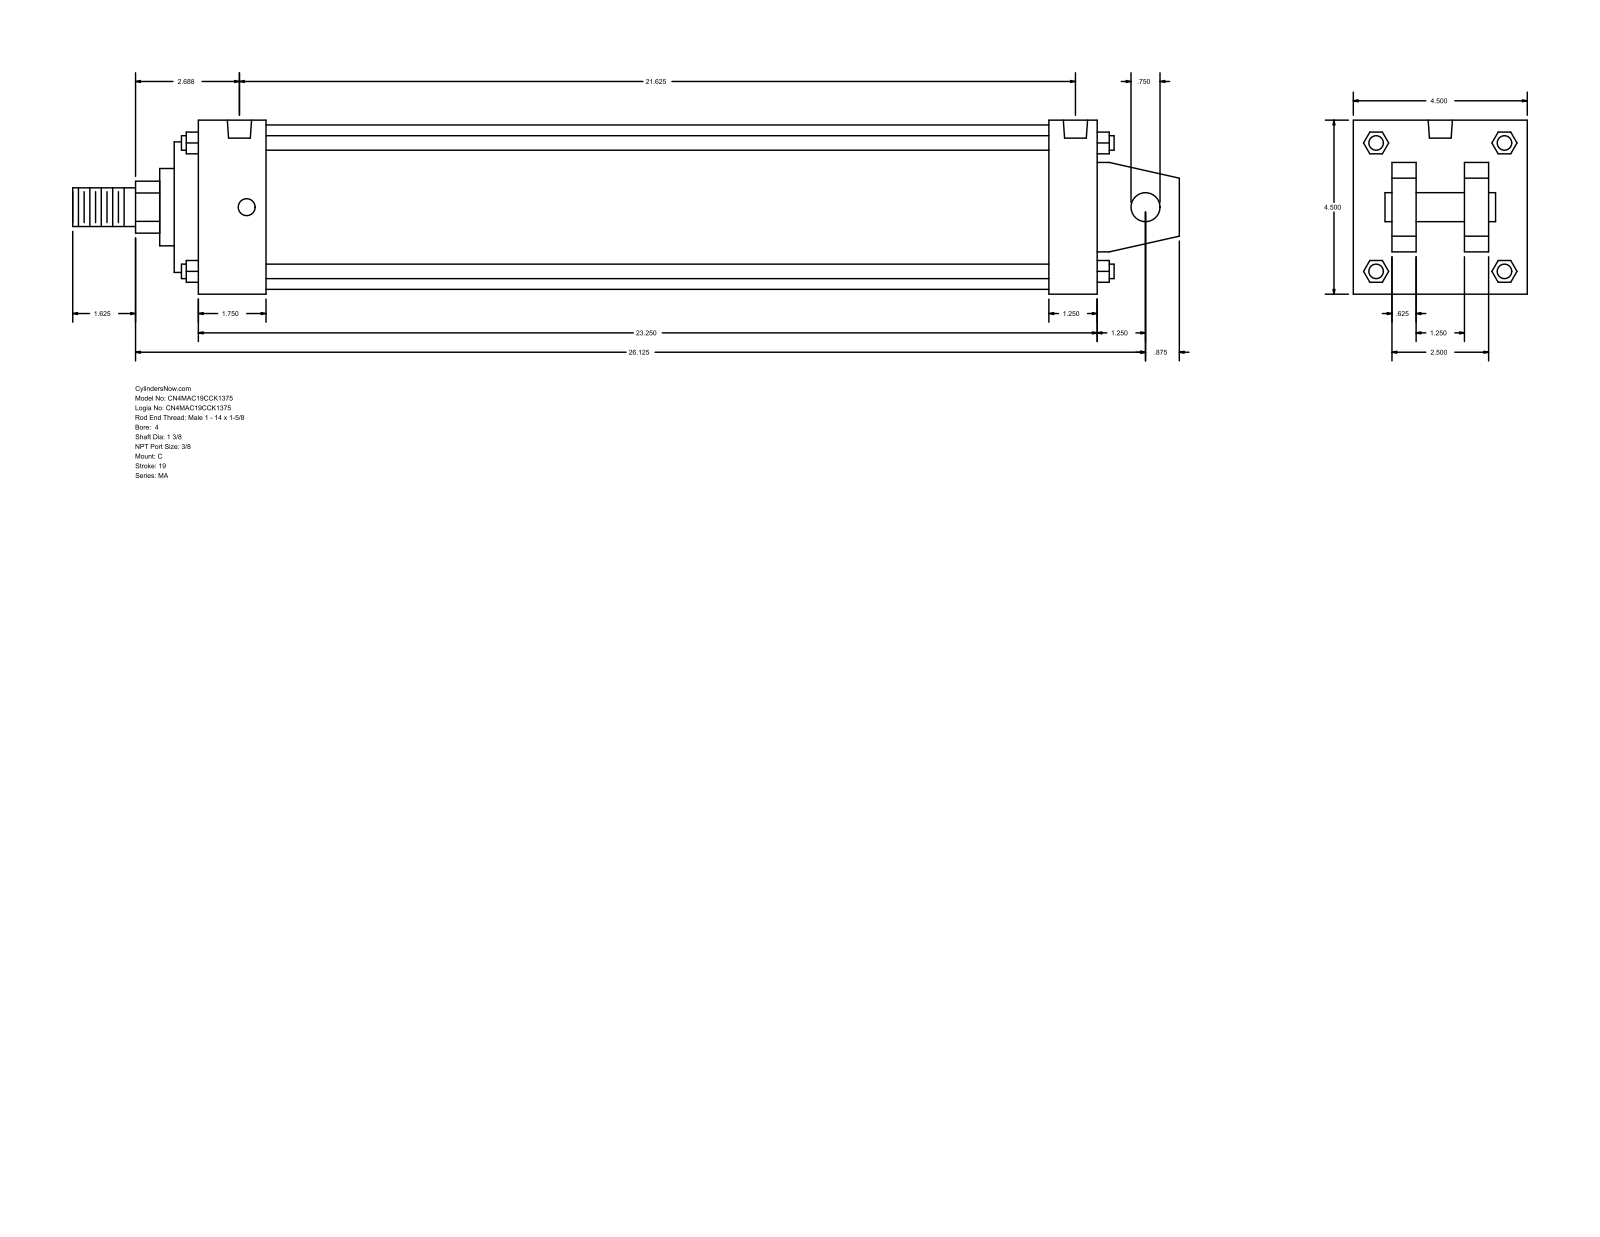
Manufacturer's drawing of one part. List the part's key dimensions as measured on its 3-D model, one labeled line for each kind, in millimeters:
Part name (STEP PRODUCT): MA_C__0400_1.375
STEP written by: GSSL Pune (CONFIG_CONTROL_DESIGN)
Units: millimetres
Bodies: 0 solids, 141 faces (109 planar, 32 cylindrical, 0 other)
Overall size (bounding box): 727.08 × 114.3 × 114.3
Round holes (diameter × count): ⌀11.11 ×4, ⌀15.93 ×2
Round bosses / shafts (diameter × count): ⌀9.53 ×4, ⌀107.95 ×1, ⌀85.72 ×1, ⌀50.8 ×1, ⌀34.92 ×1, ⌀25.4 ×1, ⌀19.05 ×1
Partial cylindrical surfaces — rounded edges, fillets, slot ends (radius × count): R17.06 ×1
Main face-to-face distances: 114.3, 15.87, 590.56, 73.03, 41.27, 25.4, 88.9, 47.63, 606.43, 574.68
Hole centre spacings: 4.77, 539.74, 544.51, 549.28
